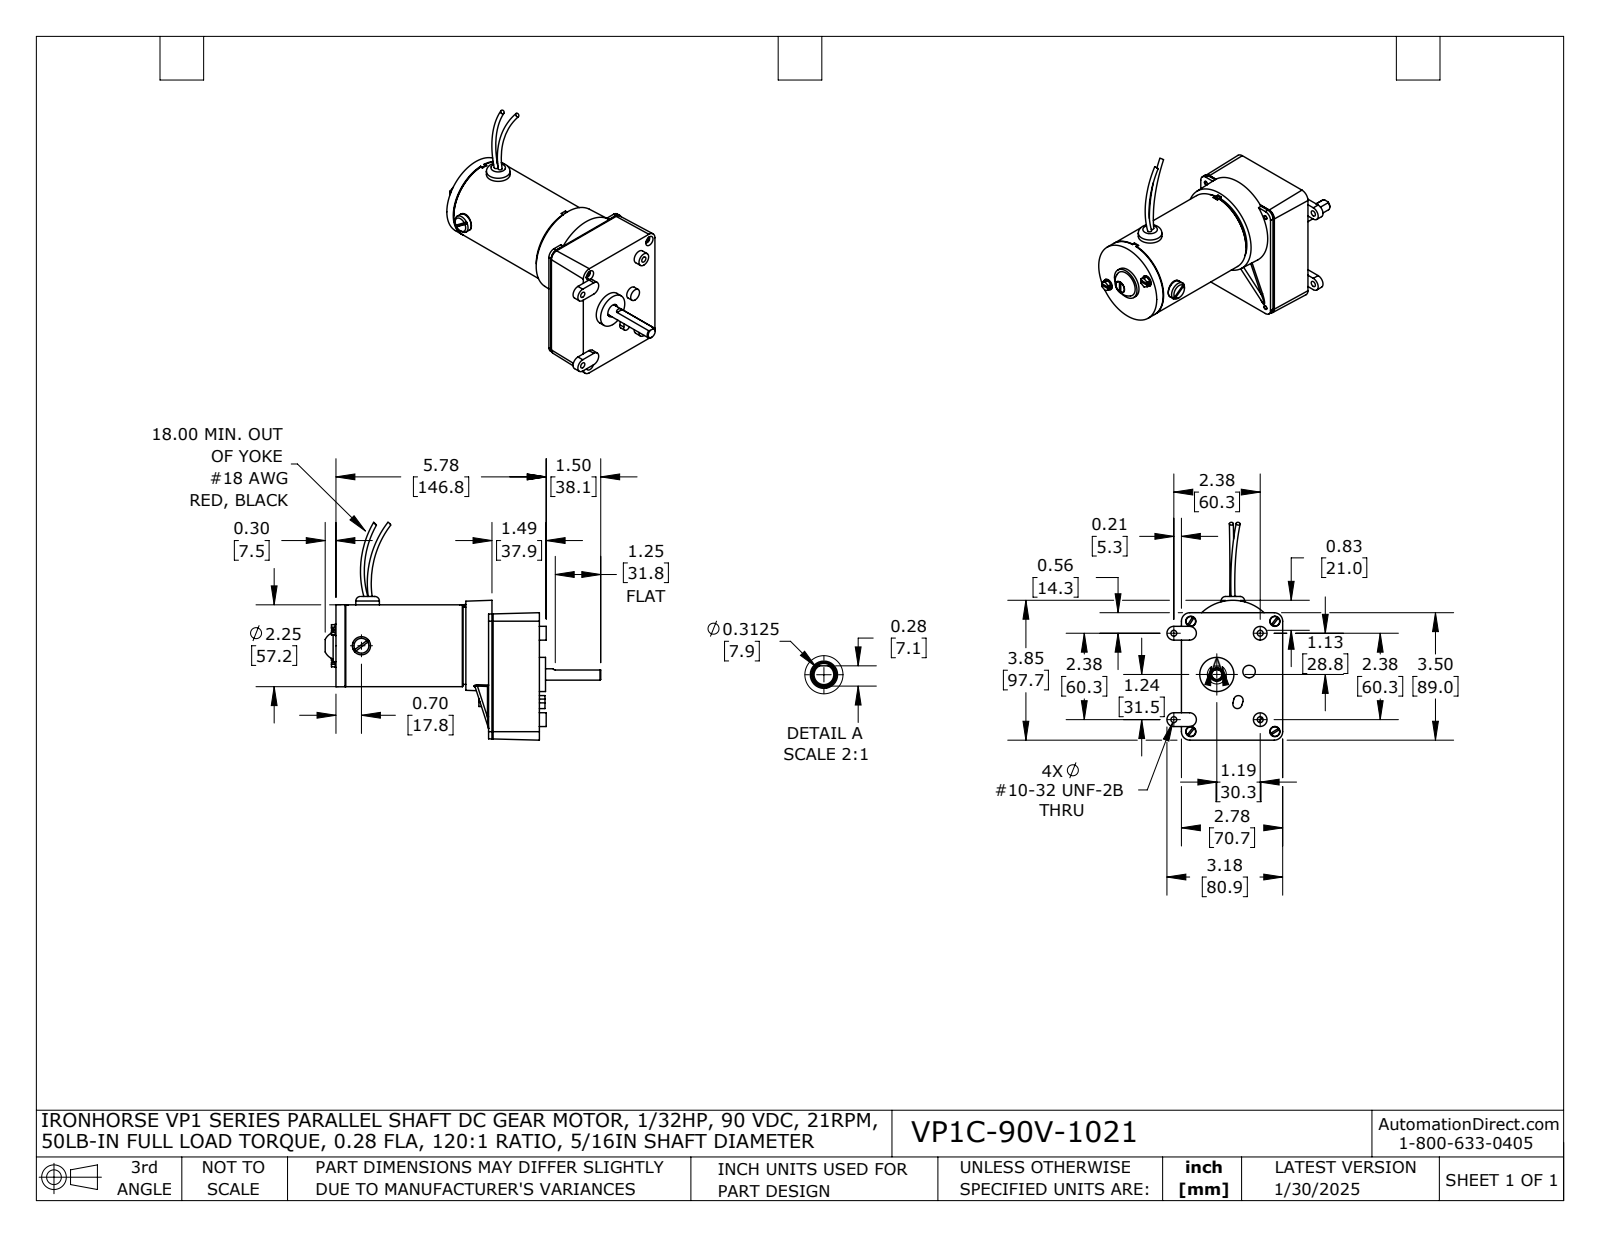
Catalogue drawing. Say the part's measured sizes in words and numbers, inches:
The part is named "VP1C-90V-1021". Its 3-D file was written by "SolidWorks 2021 (AUTOMOTIVE_DESIGN)". It is 34 solids with 1338 faces: 477 planar, 580 cylindrical and 281 other. Overall it measures 7.578 by 5.989 by 3.183 inches. Its volume is 13.71 cubic inches and its surface area 226.6 square inches. Round holes: 7 of diameter 0.281, 4 of diameter 0.037, 4 of diameter 0.117, 4 of diameter 0.149, 4 of diameter 0.15, 4 of diameter 0.161, 2 of diameter 0.125, 2 of diameter 0.187, 1 of diameter 0.127, 1 of diameter 0.127, 1 of diameter 0.213, 1 of diameter 0.239. Round bosses or shafts: 4 of diameter 0.136, 3 of diameter 0.313, 2 of diameter 0.375, 1 of diameter 2.256, 1 of diameter 2.25, 1 of diameter 2.123, 1 of diameter 2.003, 1 of diameter 2. Partial cylindrical surfaces (rounded edges, fillets, slot ends): 24 of radius 0.028, 24 of radius 0.051, 12 of radius 0.02, 12 of radius 0.055, 12 of radius 0.058, 8 of radius 0.03, 8 of radius 0.031, 8 of radius 0.19. The main face-to-face distances are 1.304, 0.097, 1.207, 1.397, 1.3, 0.093, 1.273, 1.176, 0.031, 0.124. The hole center spacings are 0.875, 0.77, 1.936, 2.31, 2.312, 3.03, 3.031, 0.135.
